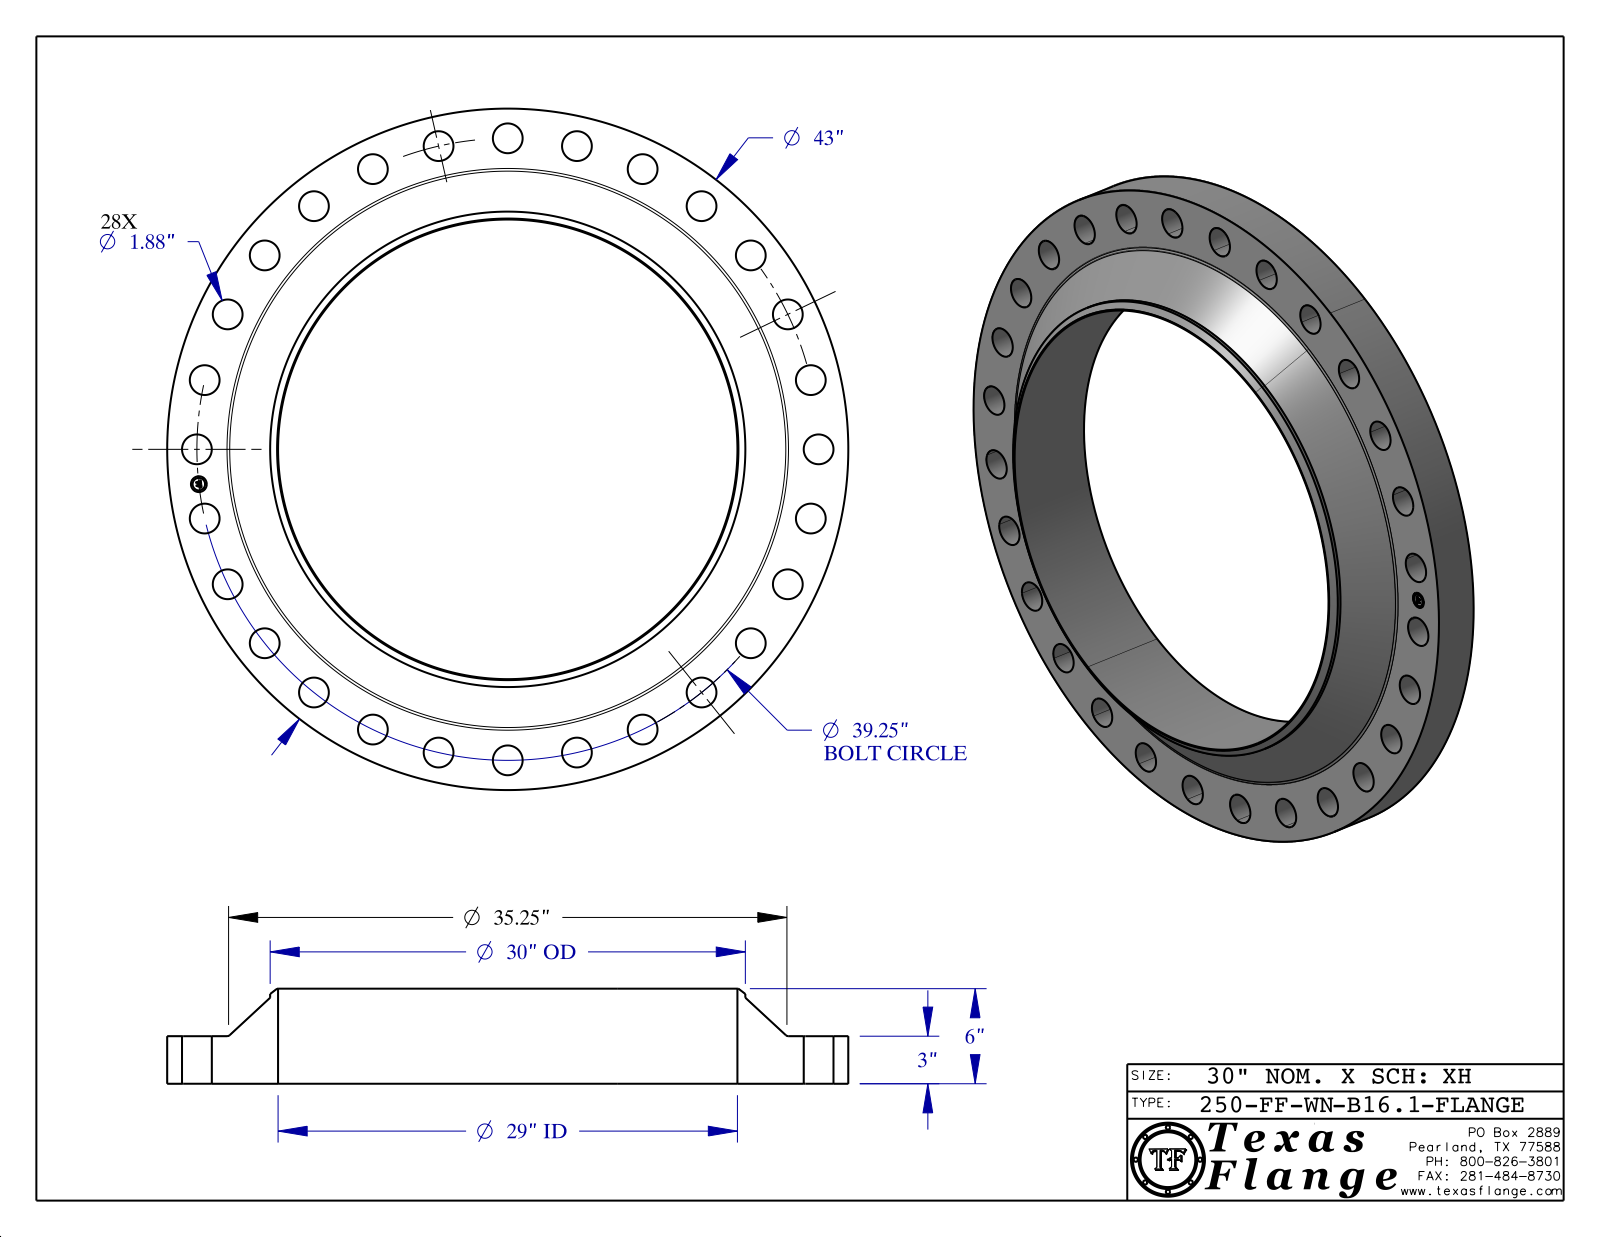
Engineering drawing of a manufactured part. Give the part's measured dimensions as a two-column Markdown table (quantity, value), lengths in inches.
| quantity | value |
| --- | --- |
| part name | 250-FF-WN, B16.1 |
| STEP written by | CATIA V5 STEP AP214 (AUTOMOTIVE_DESIGN) |
| units | inches |
| bodies | 1 solid, 456 faces (368 planar, 82 cylindrical, 6 other) |
| overall size | 43 × 43 × 6 |
| volume | 2 592 in³ |
| surface area | 3 005 in² |
| round holes (diameter × count) | 1.88 × 28, 1 × 1, 29 × 1 |
| round bosses / shafts (diameter × count) | 0.061 × 8, 43 × 1, 30 × 1, 0.788 × 1 |
| main face-to-face distances | 3, 6, 2.985, 0.015, 3.015, 0.298, 0.293, 0.054, 0.193, 0.248 |
| hole center spacings | 4.394, 8.734, 12.963, 17.03, 20.882, 35.363, 24.472, 33.234 |
